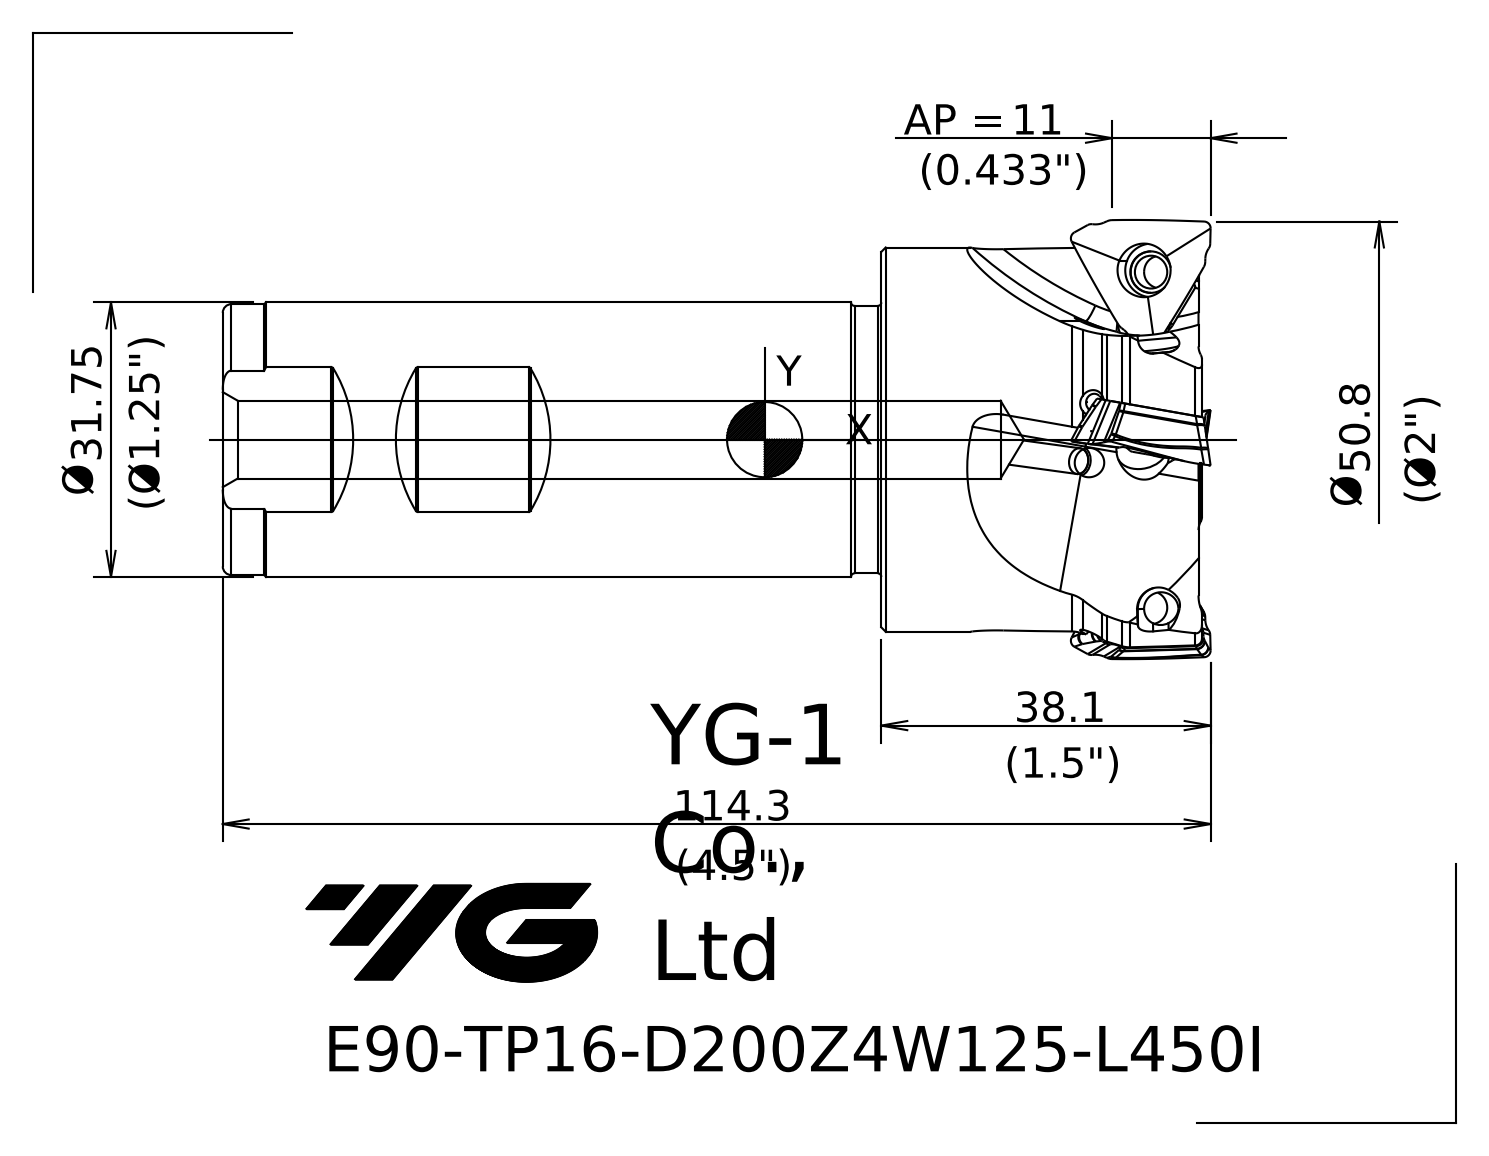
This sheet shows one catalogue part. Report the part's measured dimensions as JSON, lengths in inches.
{"part_name": "10224A3C590Cnfgp", "step_written_by": "SIEMENS PLM Software NX 10.0 (AP203_CONFIGURATION_CONTROLLED_3D_DESIGN_OF_MECHANICAL_PARTS_AND_ASSEMBLIES_MIM_LF)", "units": "inches", "bodies": {"solids": 1, "faces": 62, "planar": 10, "cylindrical": 9, "other": 43}, "overall_size": [4.5, 2.004, 2.004], "volume_in3": 6.93, "surface_area_in2": 38.68, "round_holes": [[0.059, 1], [0.354, 1]], "round_bosses_or_shafts": [[1.75, 1], [1.25, 1], [1.234, 1], [1.219, 1]], "partial_cylinders_radius": [[0.012, 3]], "face_to_face_distances": [1.445, 4.445, 3, 0.016, 1.461, 4.461, 0.079, 0.063, 1.382, 4.382]}
